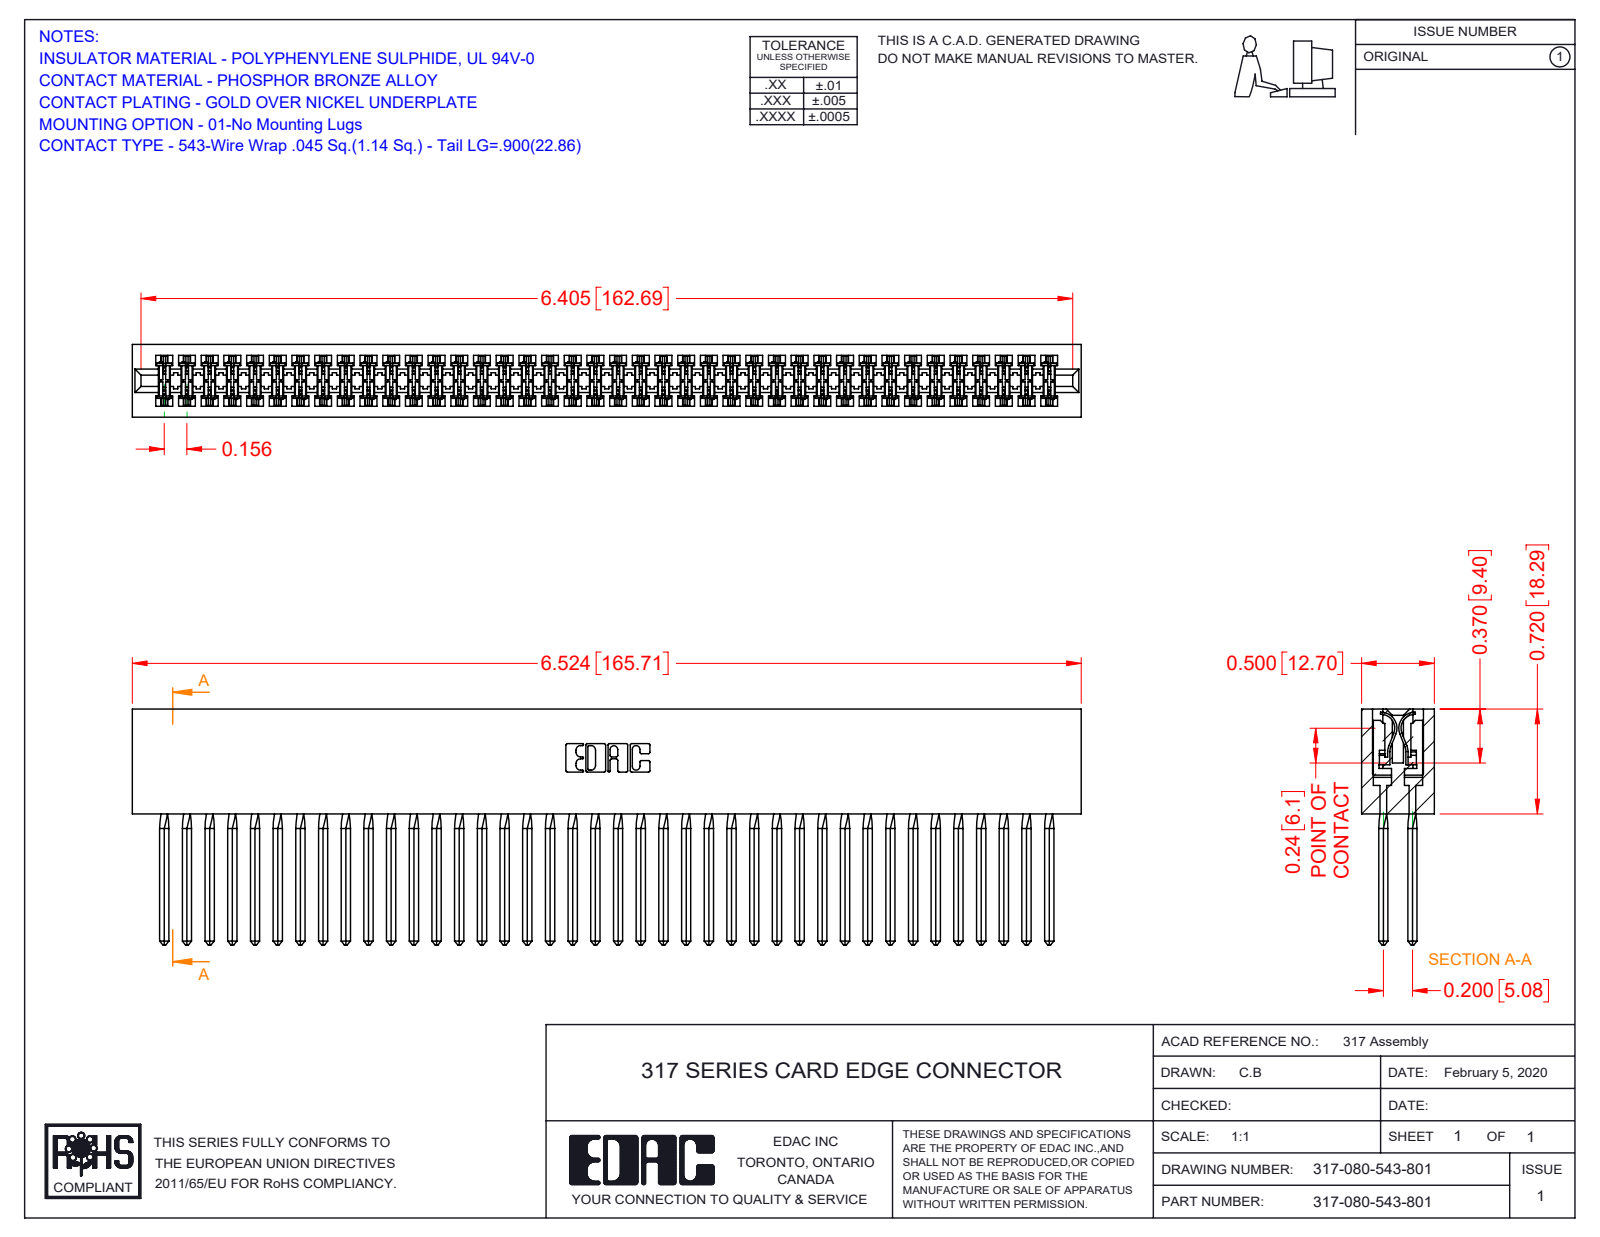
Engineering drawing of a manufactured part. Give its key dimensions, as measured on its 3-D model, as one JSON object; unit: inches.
{"part_name": "317 Part_Lugless; 317-080-543-801; 317-290-001_543", "step_written_by": "SolidWorks 2016 (CONFIG_CONTROL_DESIGN)", "units": "inches", "bodies": {"solids": 81, "faces": 7210, "planar": 5890, "cylindrical": 1000, "other": 320}, "overall_size": [6.524, 1.62, 0.5], "volume_in3": 1.827, "surface_area_in2": 70.7, "partial_cylinders_radius": [[0.015, 160], [0.01, 22], [0.007, 6], [0.031, 6], [0.026, 3], [0.095, 2], [0.1, 2], [0.11, 2]], "face_to_face_distances": [0.075, 0.5, 0.425, 0.35, 0.11, 0.195, 0.094, 0.2, 0.115, 0.131]}
